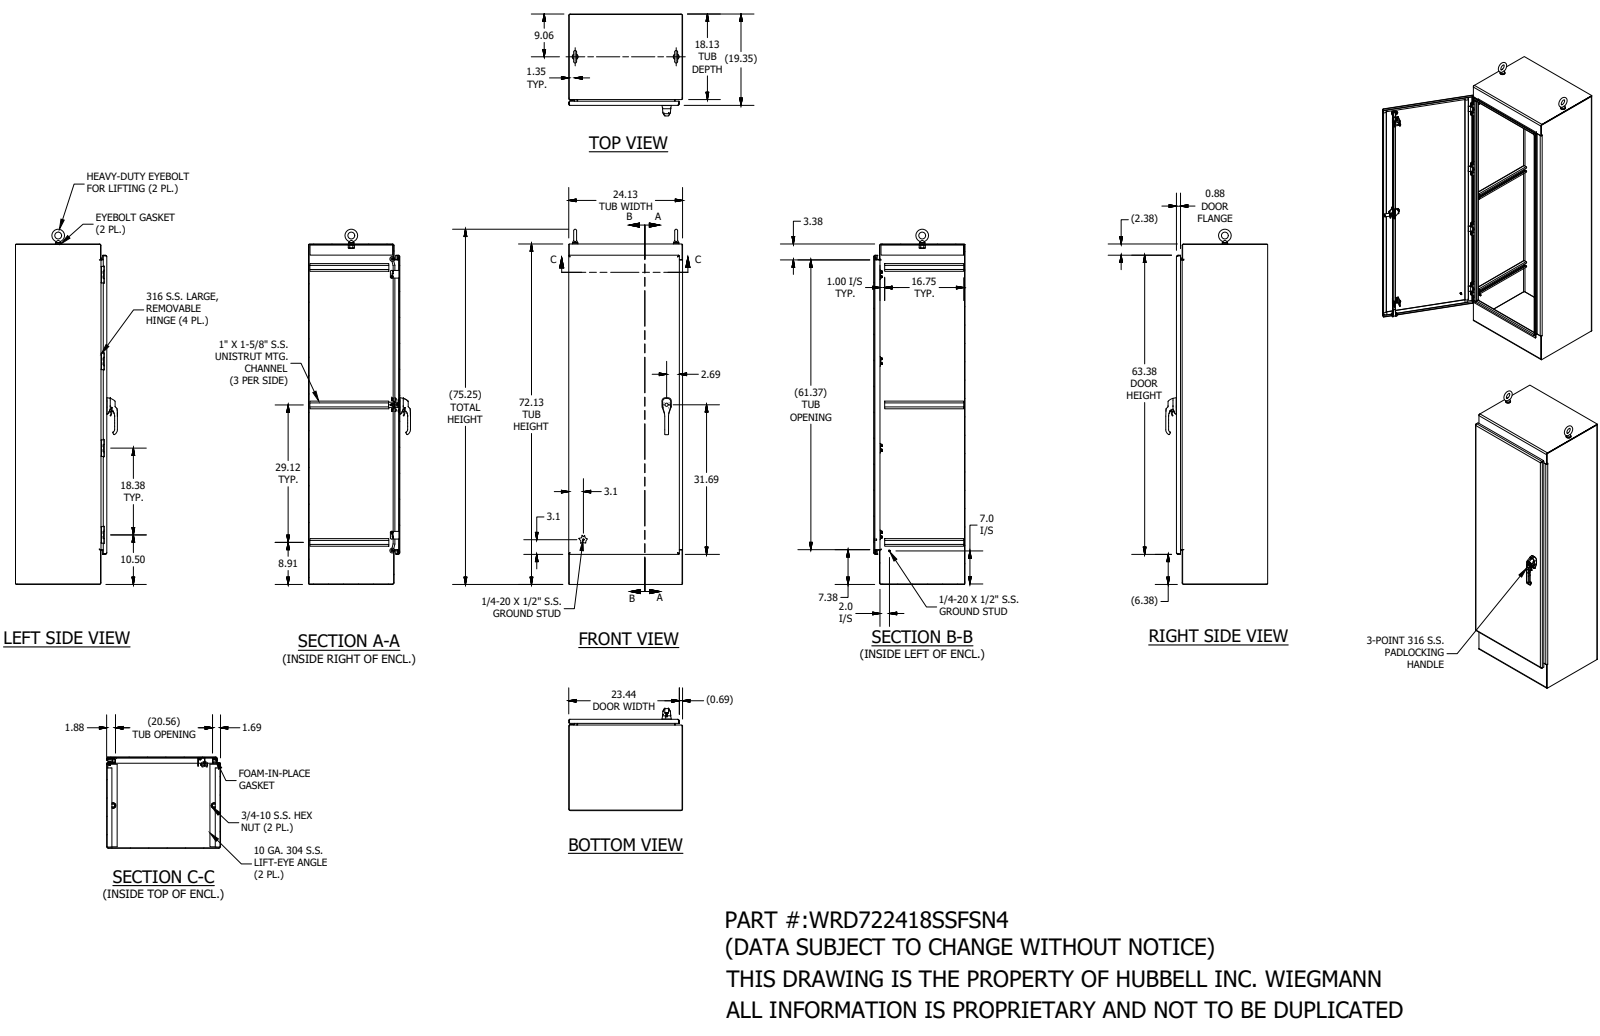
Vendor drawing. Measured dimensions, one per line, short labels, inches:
name: WRD722418SSFSN4
written by: SolidWorks 2019 (AUTOMOTIVE_DESIGN)
unit: in
bodies: 103 solids, 3881 faces (1580 planar, 1362 cylindrical, 939 other)
size: 75.248 × 24.129 × 21.598
volume: 914.3 in³; area: 16 979 in²
holes: 24× ⌀0.14, 8× ⌀0.195, 8× ⌀0.262, 8× ⌀0.266, 8× ⌀0.294, 8× ⌀0.65, 4× ⌀0.136, 4× ⌀0.164, 4× ⌀0.187, 4× ⌀0.201, 3× ⌀0.213, 3× ⌀0.281
bosses: 8× ⌀0.625, 7× ⌀0.25, 4× ⌀0.237, 3× ⌀0.236, 2× ⌀1.25, 2× ⌀1.12, 2× ⌀1, 2× ⌀0.75
rounds: 172× R0.02, 114× R0.012, 34× R0.125, 26× R0.062, 21× R0.019, 14× R0.05, 14× R0.079, 13× R0.25
face distances: 0.104, 24.021, 19.245, 19.141, 19.349, 19.245, 0.104, 23.917, 24.125, 72.021
hole spacings: 0.018, 0.012, 0.023, 0.024, 0.029, 0.38, 0.76, 1
